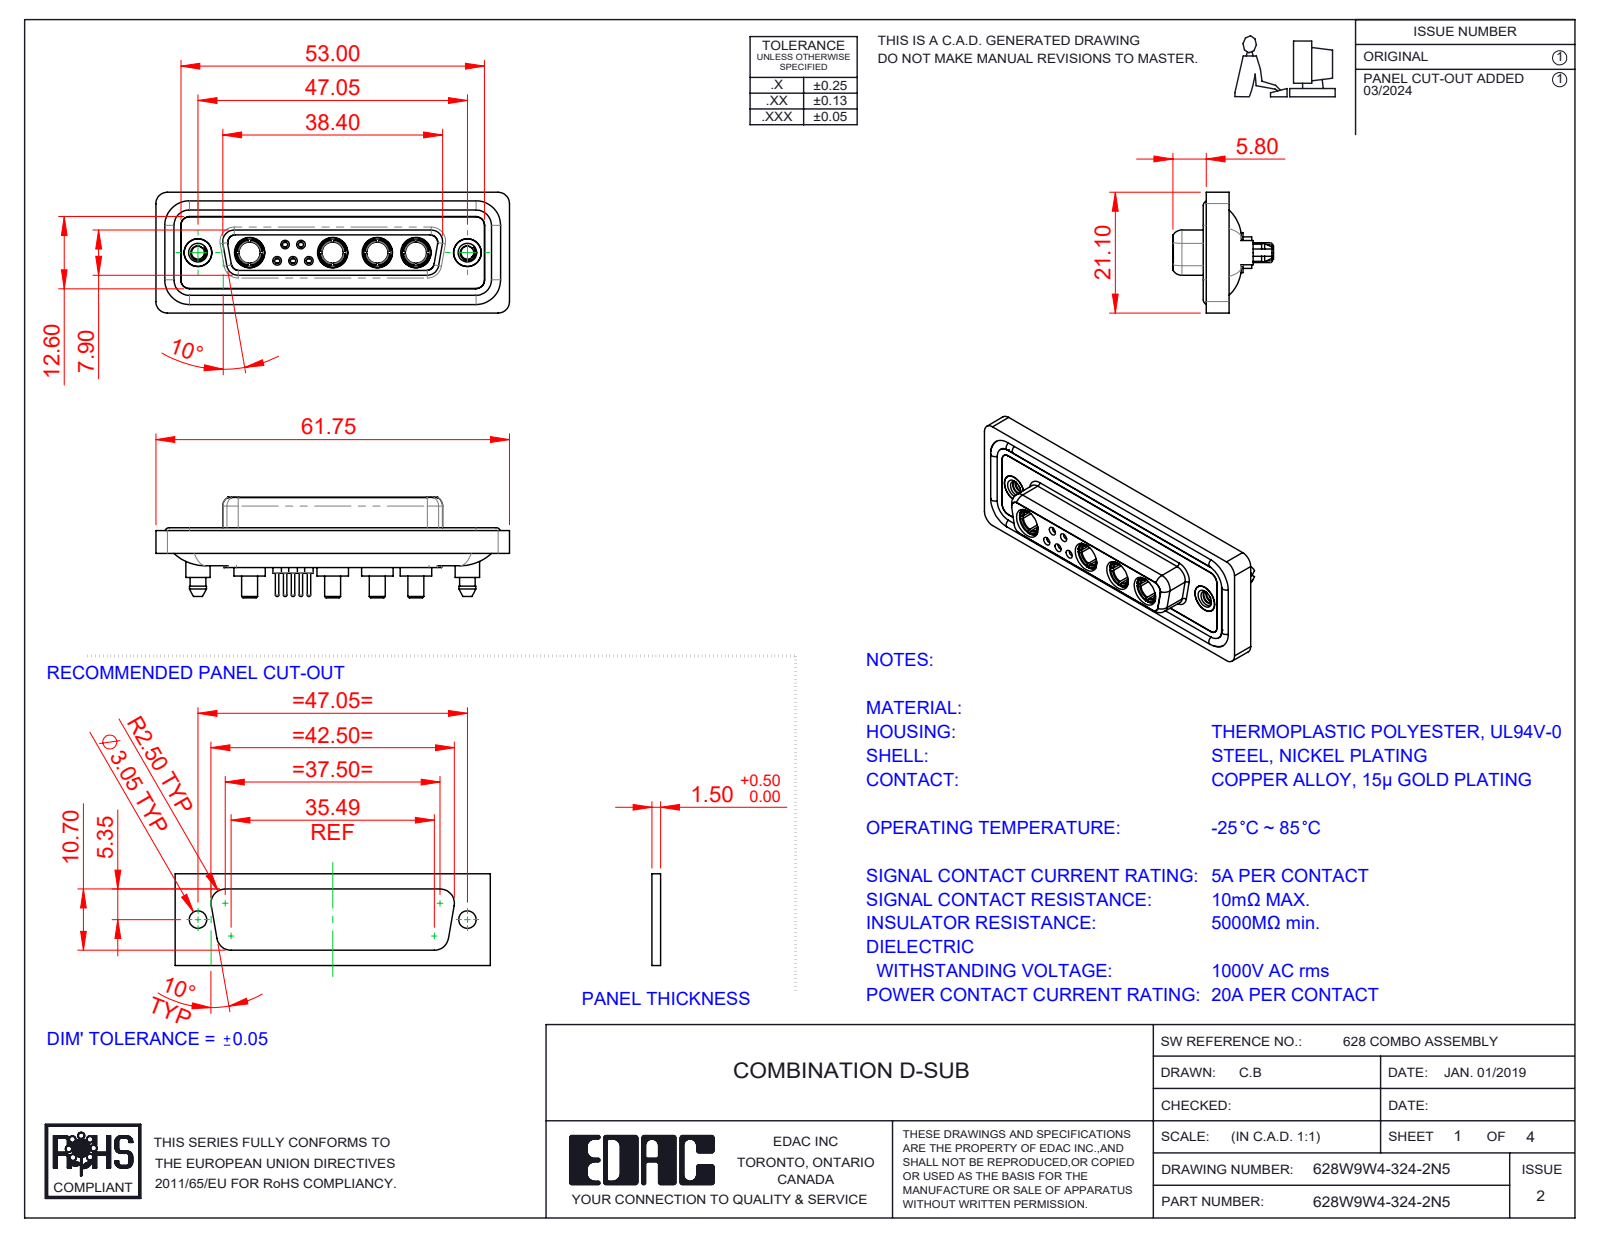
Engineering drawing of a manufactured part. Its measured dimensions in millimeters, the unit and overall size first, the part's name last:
Units: millimetres
Overall size (bounding box): 61.75 × 21.1 × 17.55
Round holes (diameter × count): ⌀4.85 ×6, ⌀0.9 ×5, ⌀1.1 ×5, ⌀1.5 ×5, ⌀2 ×5, ⌀3.7 ×4, ⌀5.3 ×4, ⌀1.6 ×3, ⌀1.7 ×2, ⌀2.26 ×2, ⌀4 ×2, ⌀4.05 ×2
Round bosses / shafts (diameter × count): ⌀1.6 ×6, ⌀2.2 ×5, ⌀0.6 ×5, ⌀5.5 ×4, ⌀5.2 ×4, ⌀4.96 ×4, ⌀4.75 ×4, ⌀3.75 ×4
Partial cylindrical surfaces — rounded edges, fillets, slot ends (radius × count): R1.5 ×24, R2 ×18, R1.6 ×10, R1.35 ×8, R0.25 ×4, R0.5 ×4, R0.6 ×4, R0.65 ×4
Main face-to-face distances: 0.4, 1.8, 7.45, 5.65, 0.5, 7.05, 6.6, 1.6, 1.1, 2.9
Hole centre spacings: 3.16, 2.77, 5.03, 2.76, 4.4, 5.02, 5.54, 5.73
Volume: 8 357 mm³ · Surface area: 13 895 mm²
Bodies: 20 solids, 1007 faces (312 planar, 407 cylindrical, 288 other)
Part name (STEP PRODUCT): Power Socket_20A S; 628Combo Contact Row 2_24; 628W9W4-324-2N5; 628Combo Threaded Boardlock_5 (+5 more)
STEP written by: SolidWorks 2023 (CONFIG_CONTROL_DESIGN)
